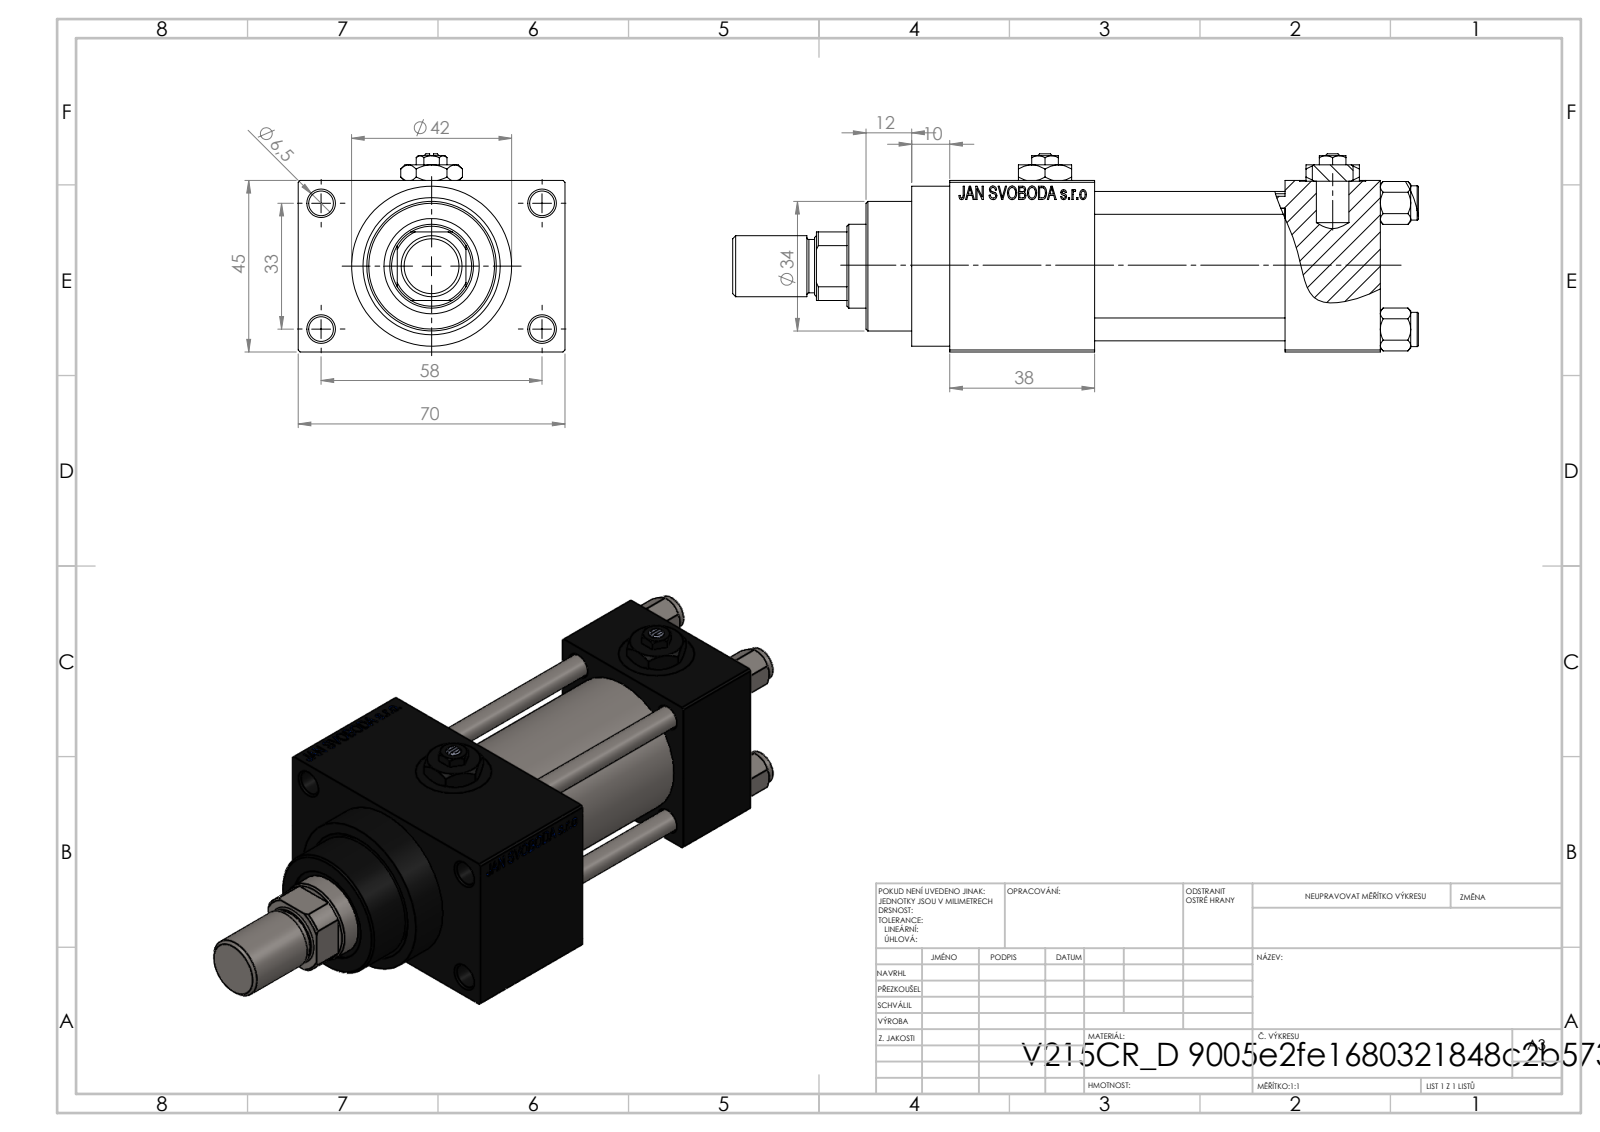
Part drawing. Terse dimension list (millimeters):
name: ROD_END_AH; V215CR_VCP_D; Zatka_pro_OIL_PORT; NUT_M5_D (+3 more)
written by: SolidWorks 2019 (CONFIG_CONTROL_DESIGN)
unit: mm
bodies: 14 solids, 1217 faces (546 planar, 103 cylindrical, 568 other)
size: 180 × 70 × 52
volume: 245 935 mm³; area: 83 165 mm²
holes: 4× ⌀6, 4× ⌀6.5, 4× ⌀13.16, 4× ⌀20, 3× ⌀7, 1× ⌀10.5, 1× ⌀22, 1× ⌀24, 1× ⌀25, 1× ⌀32, 1× ⌀33
bosses: 4× ⌀9, 1× ⌀42, 1× ⌀38, 1× ⌀34, 1× ⌀16, 1× ⌀14
rounds: 1× R10.5
face distances: 45, 25, 50, 12.5, 75, 57.5, 88, 38, 113, 70
hole spacings: 12.4, 23.48, 33.2, 33.37, 35.35, 45.6, 56.35, 33
